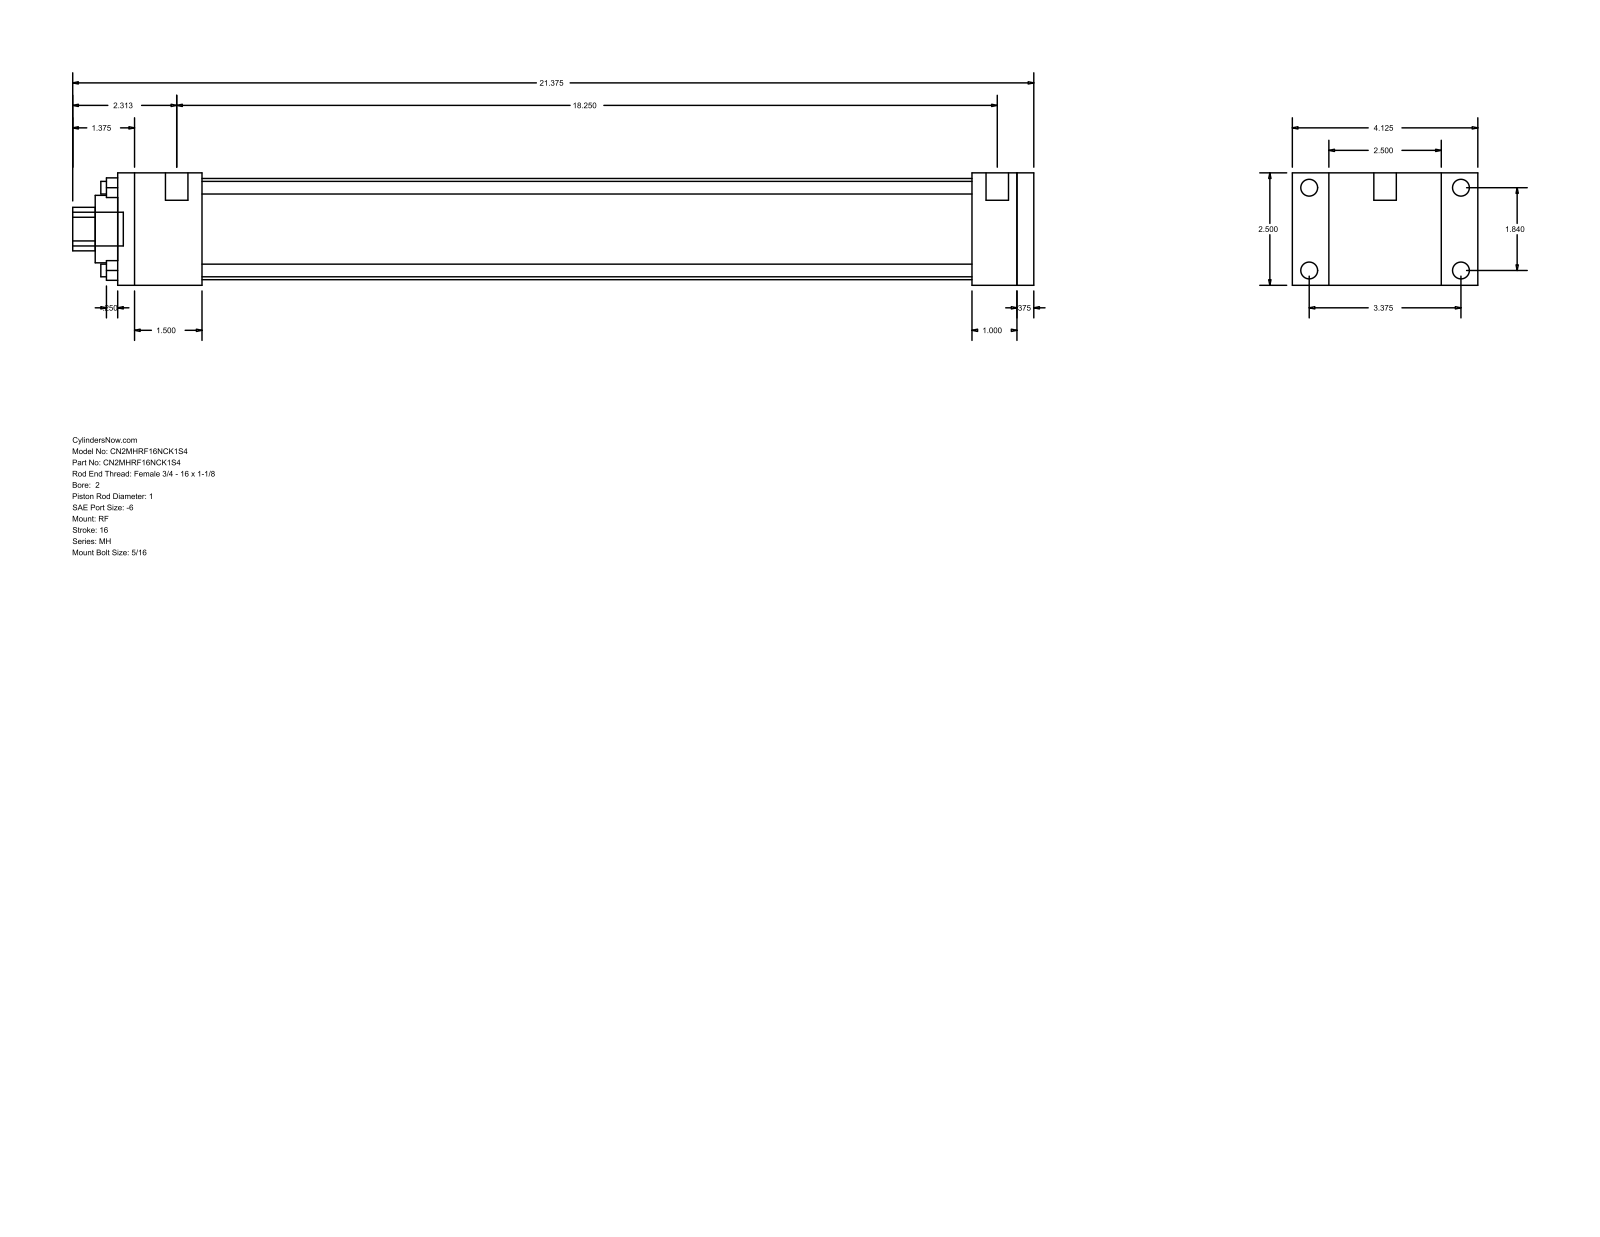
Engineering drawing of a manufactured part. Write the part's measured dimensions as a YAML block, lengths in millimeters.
part_name: "MH_RF__0200_1"
step_written_by: "GSSL Pune (CONFIG_CONTROL_DESIGN)"
units: millimeters
bodies: {solids: 0, faces: 92, planar: 64, cylindrical: 28, other: 0}
overall_size: [542.92, 104.78, 63.5]
round_holes:
  - {diameter: 7.14, count: 4}
  - {diameter: 25.4, count: 1}
  - {diameter: 38.1, count: 1}
  - {diameter: 57.15, count: 1}
round_bosses_or_shafts:
  - {diameter: 9.53, count: 4}
  - {diameter: 5.56, count: 4}
  - {diameter: 12.7, count: 2}
  - {diameter: 19.05, count: 1}
partial_cylinders:
  - {radius: 12.29, count: 1}
face_to_face_distances: [63.5, 9.52, 517.52, 508, 20.64, 25.4, 47.63, 482.6, 434.97, 460.37]
hole_center_spacings: [33.05, 46.74, 66.1]
